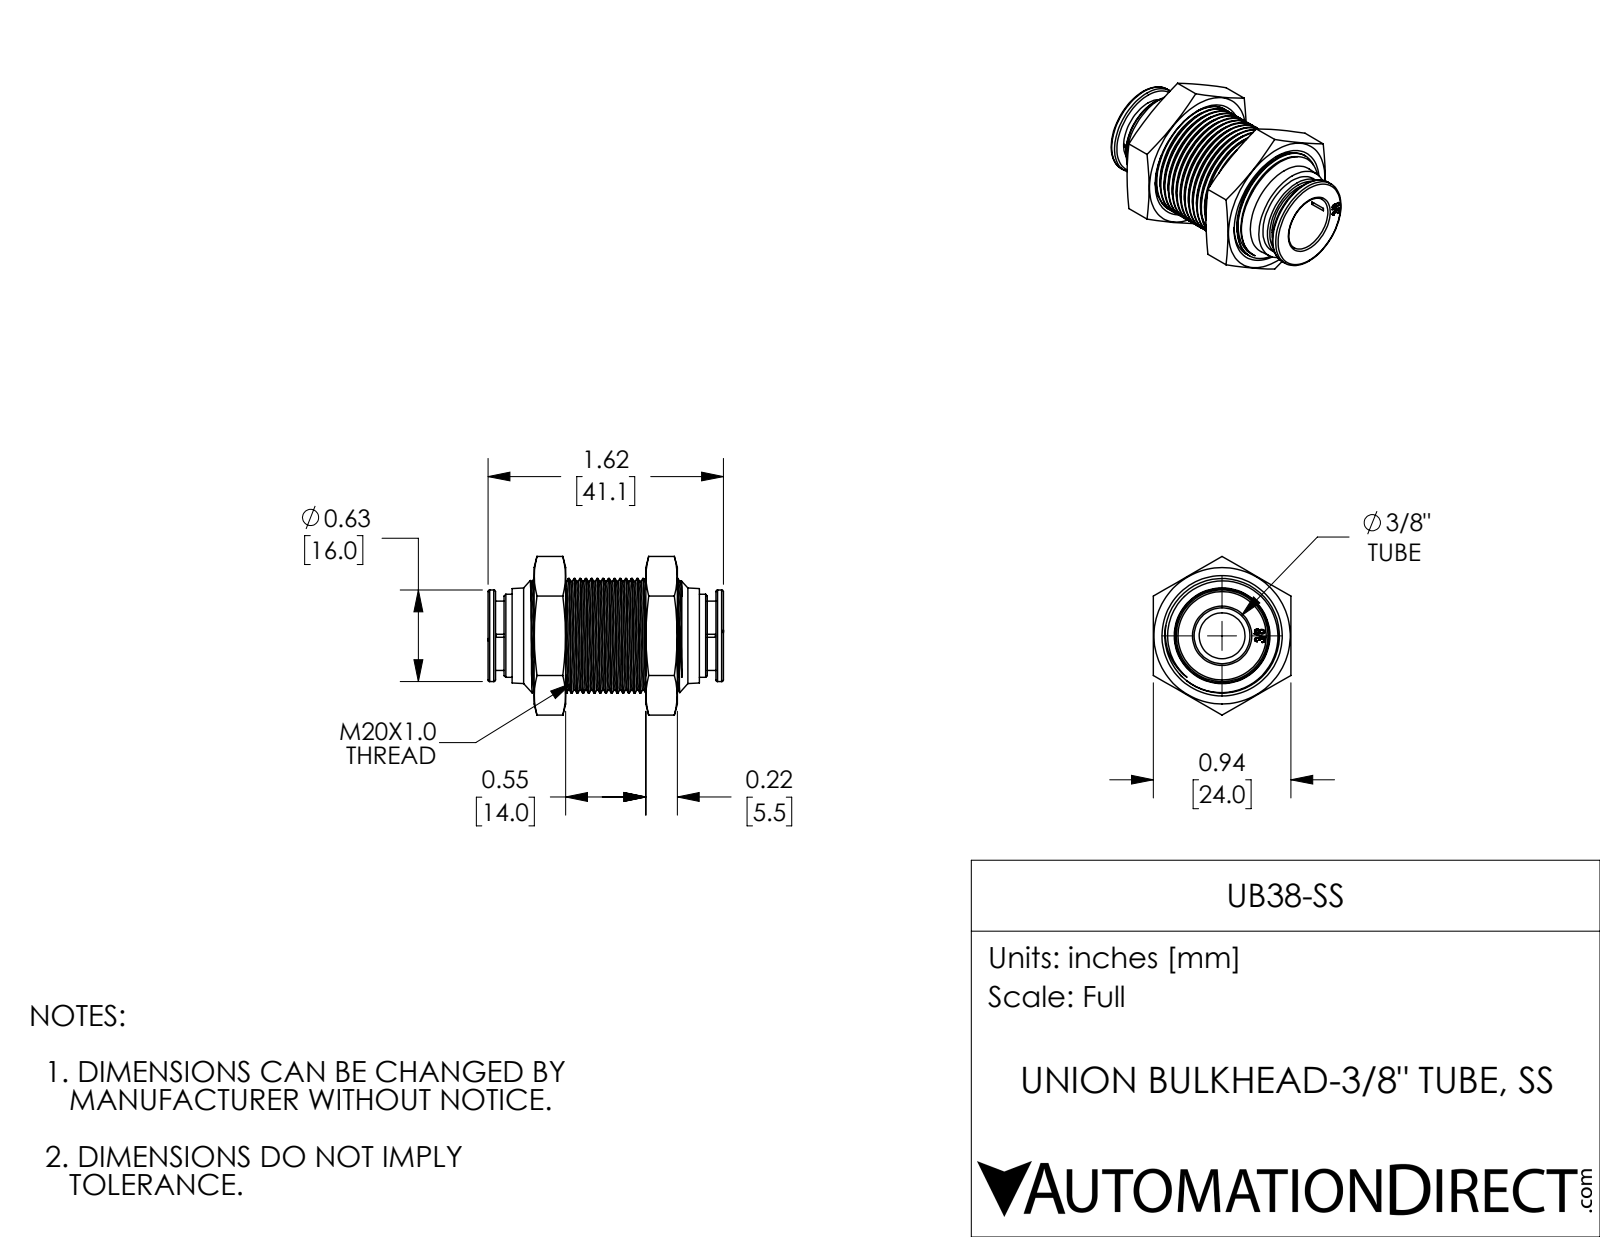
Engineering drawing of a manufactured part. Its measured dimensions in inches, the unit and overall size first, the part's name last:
Units: inches
Overall size (bounding box): 1.618 × 1.091 × 0.945
Round holes (diameter × count): ⌀0.315 ×1, ⌀0.384 ×1
Round bosses / shafts (diameter × count): ⌀0.787 ×1, ⌀0.748 ×1, ⌀0.63 ×1, ⌀0.571 ×1, ⌀0.476 ×1
Main face-to-face distances: 0.945, 0.317, 0.533, 1.085, 1.301, 0.217, 0.768, 0.051, 1.567, 0.266
Volume: 0.589 in³ · Surface area: 9.915 in²
Bodies: 1 solid, 285 faces (64 planar, 99 cylindrical, 122 other)
Part name (STEP PRODUCT): UB38-SS
STEP written by: SolidWorks 2017 (AUTOMOTIVE_DESIGN)
